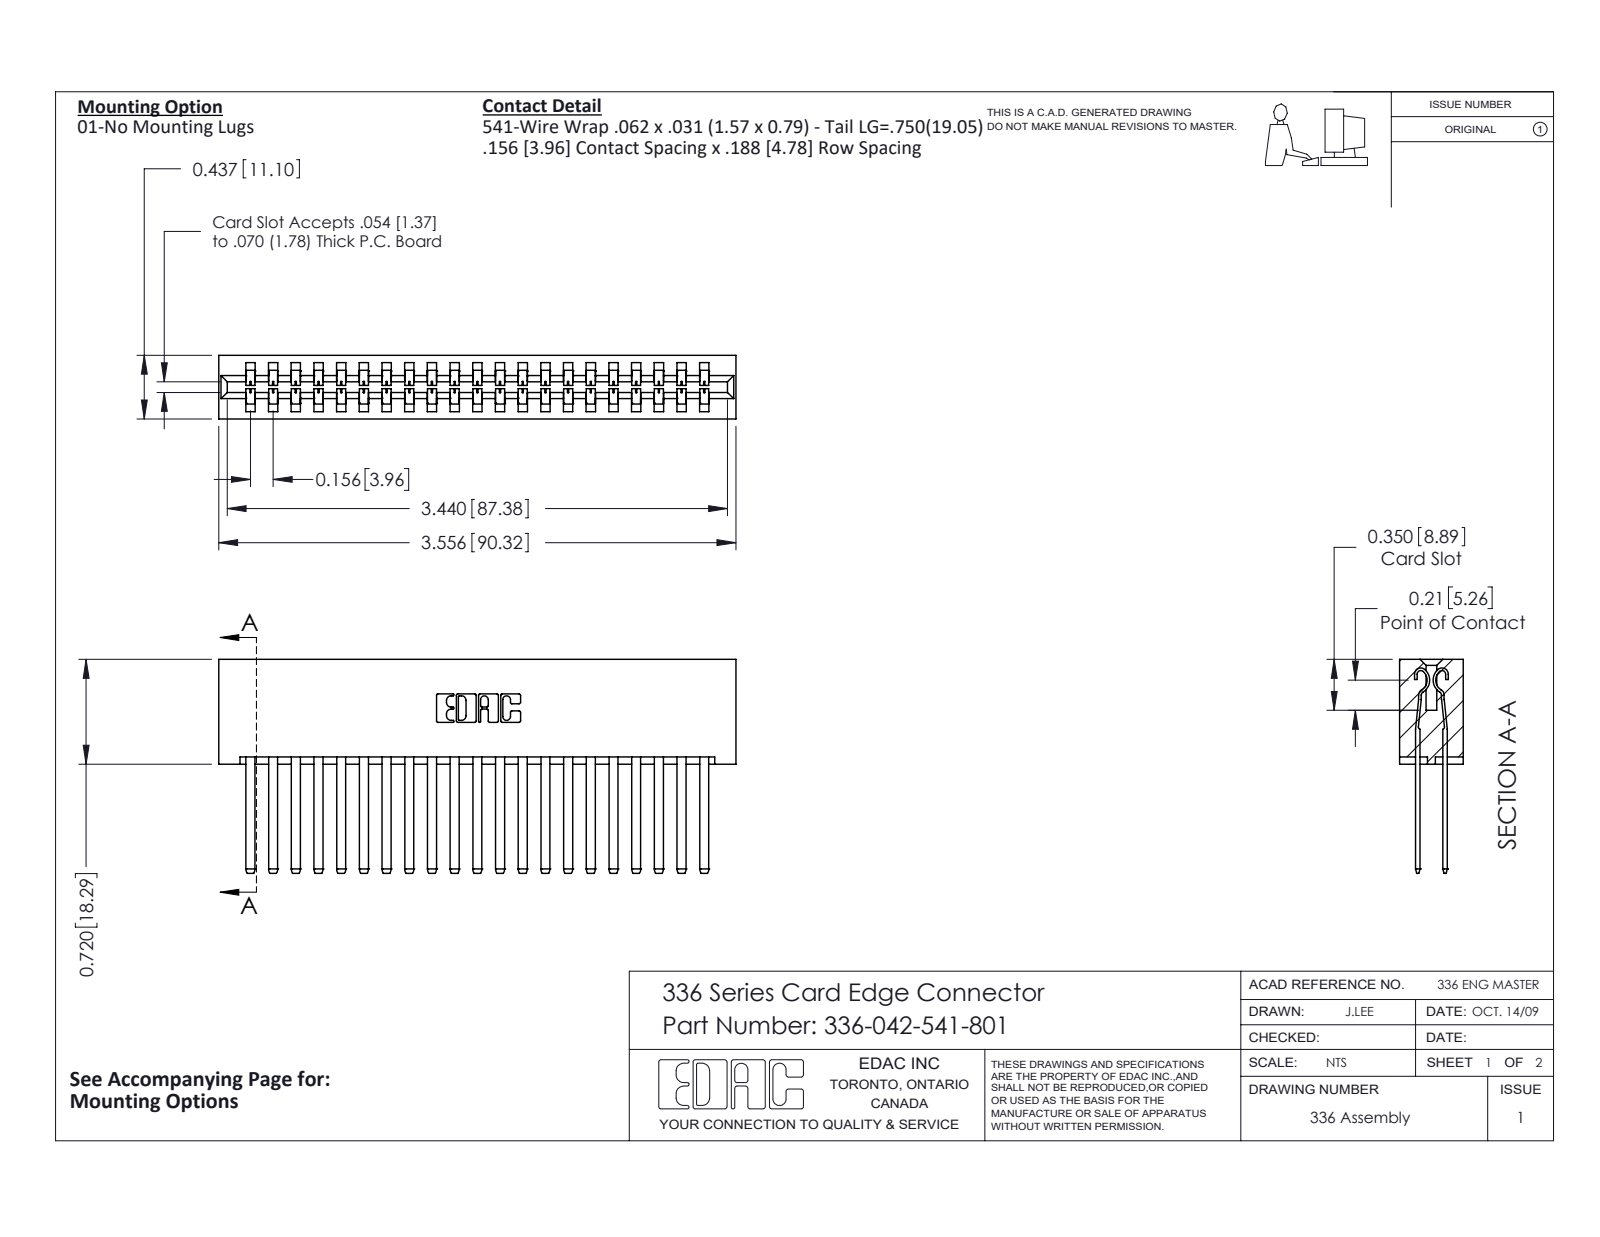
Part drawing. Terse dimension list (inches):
name: 336-290-001_336-290-541; 336 Part_Lugless; 336-042-541-801
written by: SolidWorks 2020 (CONFIG_CONTROL_DESIGN)
unit: in
bodies: 43 solids, 1870 faces (1158 planar, 712 cylindrical, 0 other)
size: 3.556 × 1.47 × 0.437
volume: 0.912 in³; area: 29.24 in²
rounds: 84× R0.004, 42× R0.056, 22× R0.01, 6× R0.007, 6× R0.031, 4× R0.022, 4× R0.04, 3× R0.026
face distances: 0.188, 0.328, 0.14, 0.297, 0.109, 0.031, 0.437, 0.033, 0.181, 0.256
